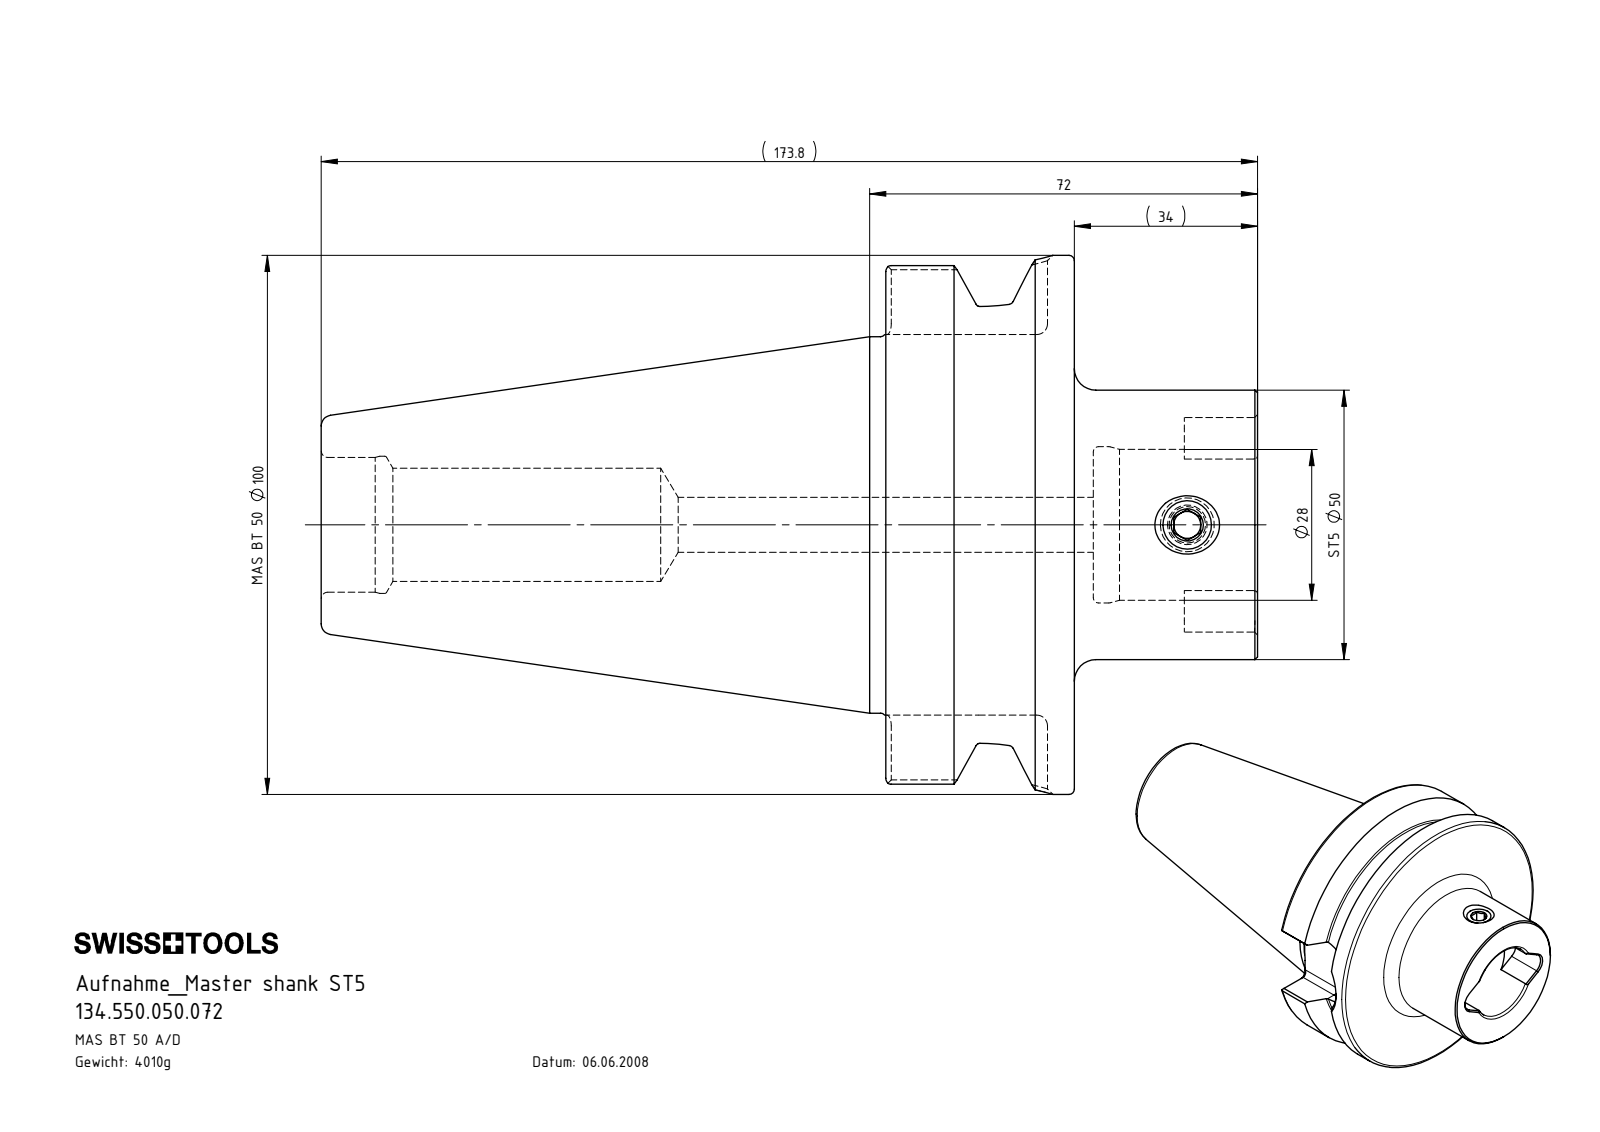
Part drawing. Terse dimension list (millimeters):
name: ST5-ER1.001.012_A; BT5.ST5.K01.072; BT5-ST5.K01.072_B
written by: SolidWorks 2017 (AUTOMOTIVE_DESIGN)
unit: mm
bodies: 2 solids, 109 faces (42 planar, 28 cylindrical, 39 other)
size: 173.8 × 100 × 100
volume: 510 838 mm³; area: 59 745 mm²
holes: 1× ⌀5, 1× ⌀9, 1× ⌀10.2, 1× ⌀21, 1× ⌀25, 1× ⌀25.45, 1× ⌀28, 1× ⌀29
bosses: 1× ⌀100, 1× ⌀85, 1× ⌀69.85, 1× ⌀50, 1× ⌀10
rounds: 8× R2, 2× R4.2, 1× R12.85
face distances: 35, 69, 34, 70.6, 38.5, 3.5, 30.5, 104.8, 139.8, 143.3
